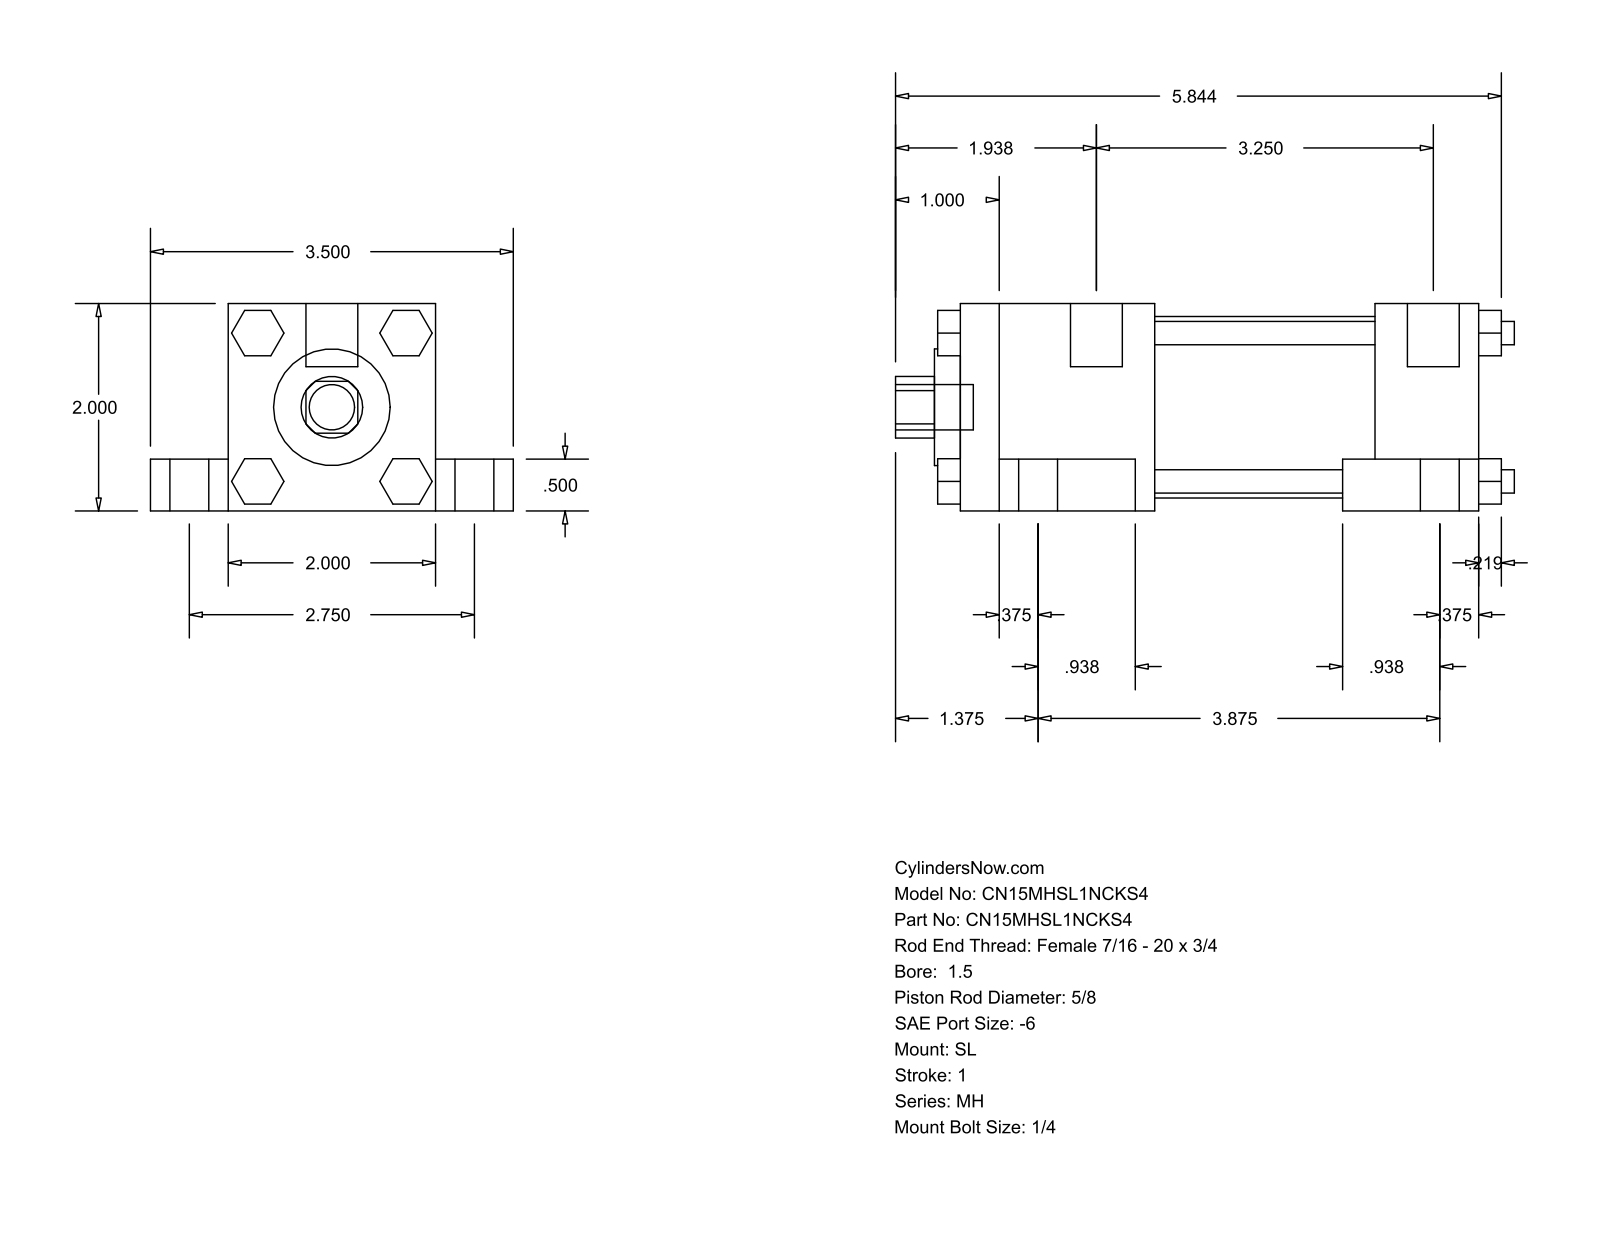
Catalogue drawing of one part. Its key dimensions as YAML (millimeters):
part_name: "MH_SL__0150_0.625"
step_written_by: "GSSL Pune (CONFIG_CONTROL_DESIGN)"
units: millimeters
bodies: {solids: 0, faces: 148, planar: 112, cylindrical: 36, other: 0}
overall_size: [151.61, 88.9, 50.8]
round_holes:
  - {diameter: 15.88, count: 1}
  - {diameter: 28.57, count: 1}
  - {diameter: 44.45, count: 1}
round_bosses_or_shafts:
  - {diameter: 15.88, count: 4}
  - {diameter: 9.53, count: 4}
  - {diameter: 5.71, count: 4}
  - {diameter: 5.56, count: 4}
  - {diameter: 12.7, count: 2}
  - {diameter: 11.11, count: 1}
partial_cylinders:
  - {radius: 7.54, count: 1}
face_to_face_distances: [50.8, 38.1, 19.05, 12.7, 69.85, 127, 53.97, 9.52, 33.34, 84.14]
